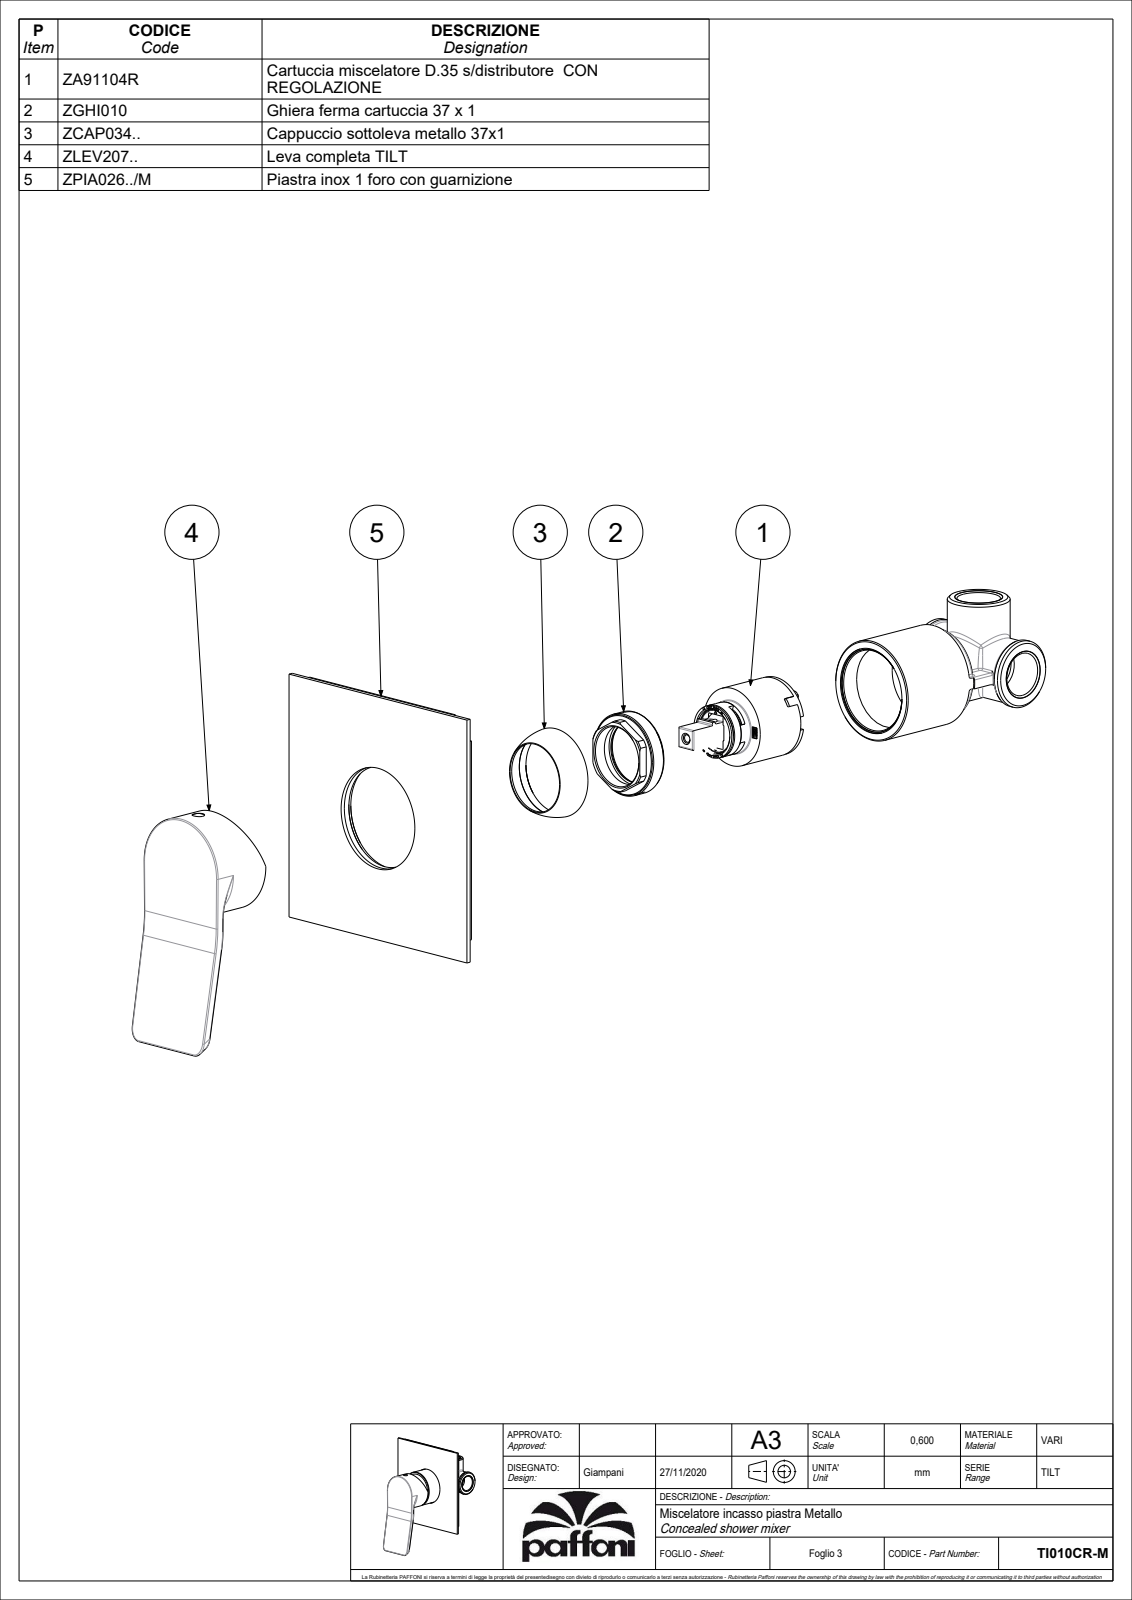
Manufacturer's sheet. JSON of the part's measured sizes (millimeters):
{"part_name": "TI010CR-M", "step_written_by": "CREO PARAMETRIC BY PTC INC, 2020044 (CONFIG_CONTROL_DESIGN)", "units": "millimeters", "bodies": {"solids": 0, "faces": 60, "planar": 18, "cylindrical": 20, "other": 22}, "overall_size": [134.58, 110, 63.05], "round_bosses_or_shafts": [[45.5, 1], [44.8, 1], [7.6, 1]], "partial_cylinders_radius": [[0.5, 10], [5, 2], [44.14, 1], [63, 1]], "face_to_face_distances": [2, 4.01, 54.1, 52.1, 22, 20, 32.1, 110, 24.1, 22.1]}
